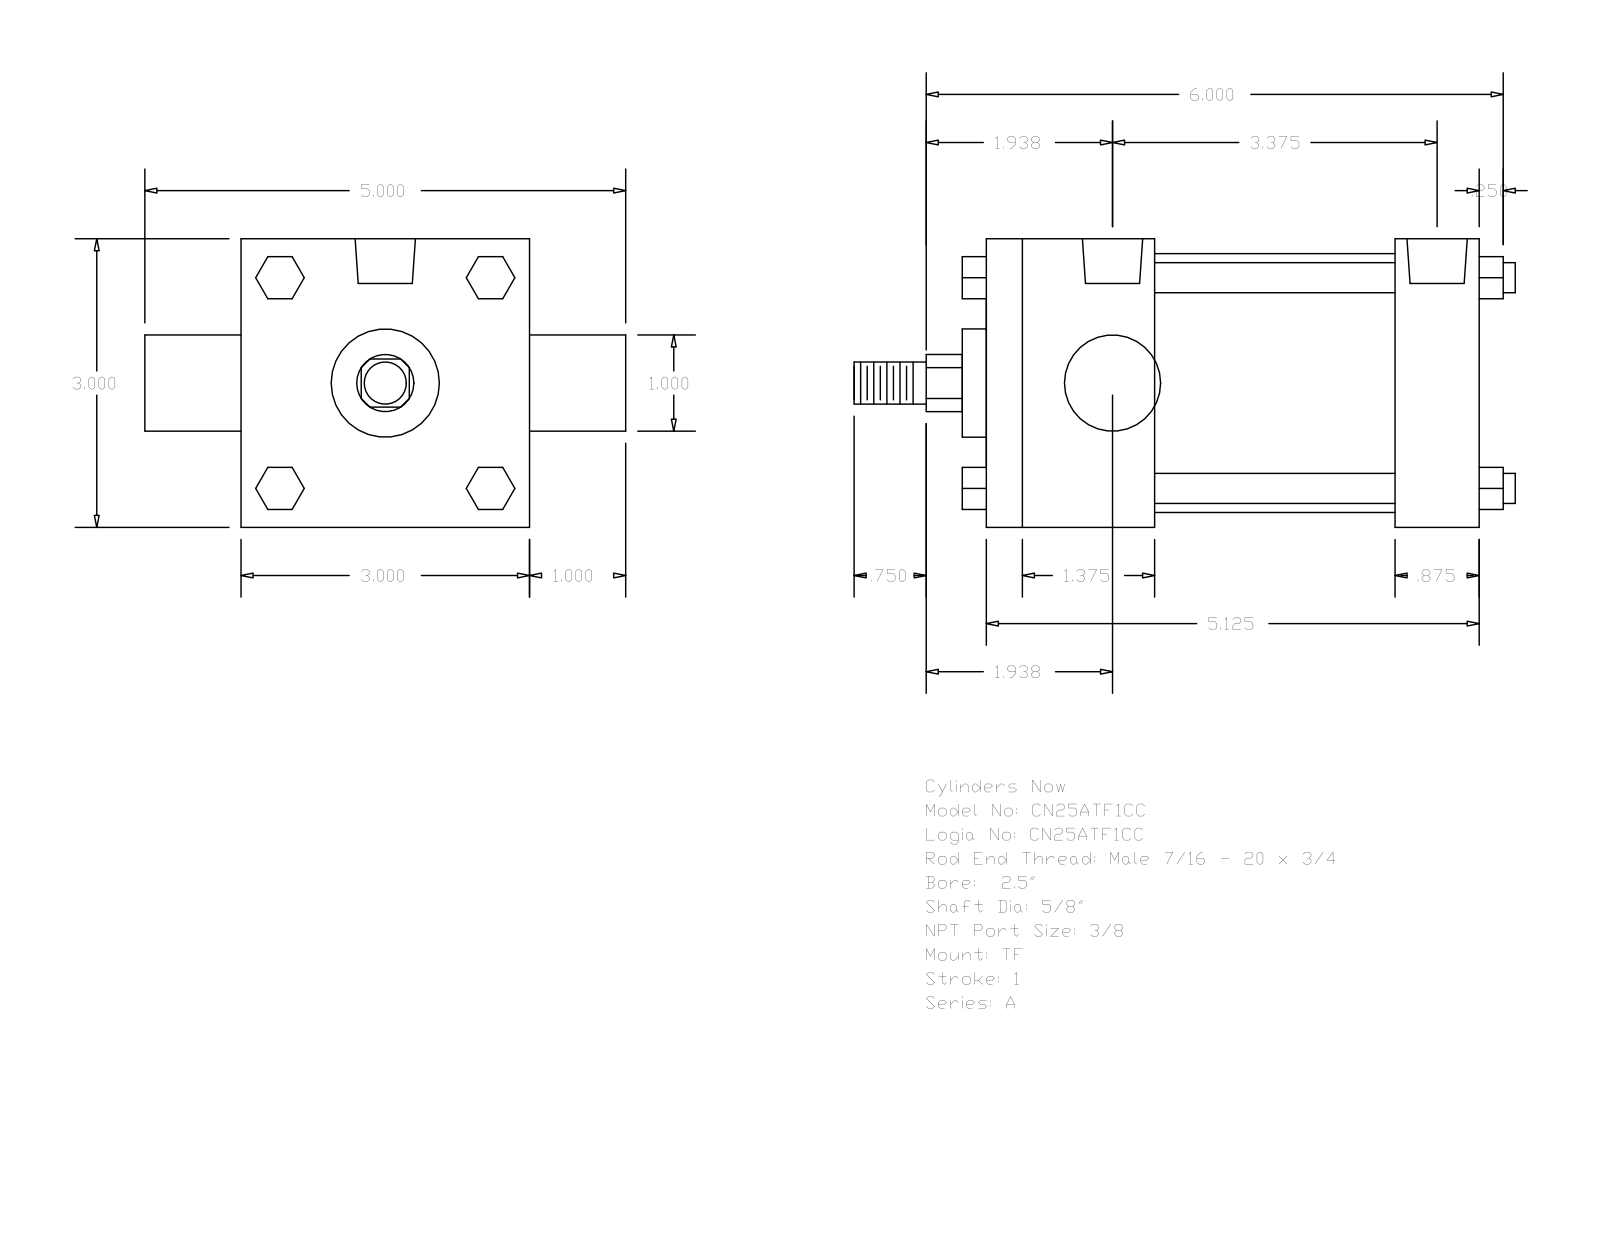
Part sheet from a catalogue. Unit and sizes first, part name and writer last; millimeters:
Units: millimetres
Overall size (bounding box): 174.62 × 127 × 76.2
Round holes (diameter × count): ⌀5.56 ×3, ⌀15.93 ×2
Round bosses / shafts (diameter × count): ⌀7.94 ×4, ⌀68.33 ×1, ⌀28.57 ×1, ⌀25.4 ×1, ⌀15.88 ×1, ⌀11.11 ×1
Partial cylindrical surfaces — rounded edges, fillets, slot ends (radius × count): R7.54 ×1
Main face-to-face distances: 76.2, 130.17, 44.45, 107.95, 63.5, 85.72, 22.22, 25.4, 101.6, 6.35
Hole centre spacings: 2.38, 88.11, 85.73, 90.49
Bodies: 0 solids, 120 faces (92 planar, 28 cylindrical, 0 other)
Part name (STEP PRODUCT): A_TF__0250_0.625
STEP written by: GSSL Pune (CONFIG_CONTROL_DESIGN)
